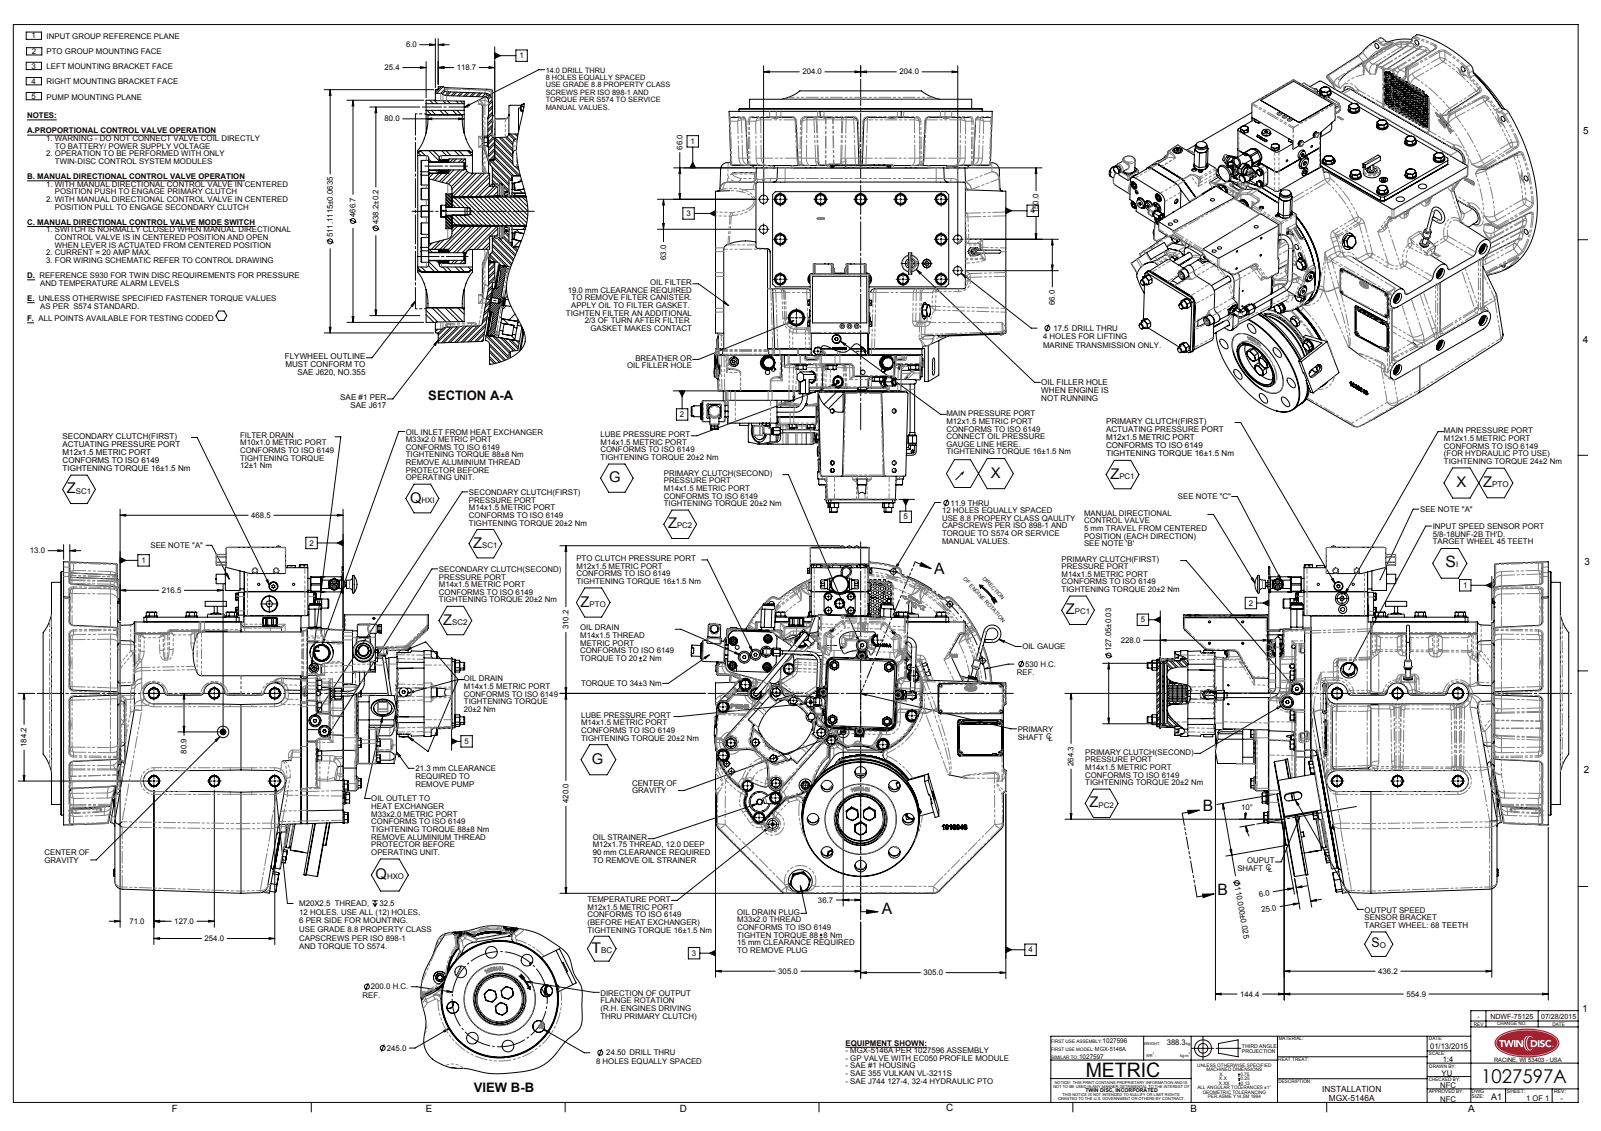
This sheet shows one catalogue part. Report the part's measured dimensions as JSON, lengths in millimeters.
{"part_name": "1027597A", "step_written_by": "SolidWorks 2010 (AUTOMOTIVE_DESIGN)", "units": "millimeters", "bodies": {"solids": 0, "faces": 5019, "planar": 1652, "cylindrical": 1588, "other": 1779}, "overall_size": [885.73, 730.22, 663.79], "round_holes": [[7, 90], [11.91, 12], [25, 9], [4.2, 8], [14, 8], [24.5, 8], [8.8, 6], [23.51, 6], [20, 5], [12, 4], [14.34, 4], [17.5, 4]], "round_bosses_or_shafts": [[24, 42], [18.9, 10], [6.35, 6], [19.05, 5], [16.8, 5], [13, 5], [12, 5], [2.54, 5]], "partial_cylinders_radius": [[3, 83], [8, 75], [2.5, 73], [6.5, 48], [16, 32], [2, 28], [3.05, 27], [6, 21]], "face_to_face_distances": [0.39, 13.09, 75, 75.39, 479.48, 404.48, 404.09, 88.48, 13.48, 391], "hole_center_spacings": [20, 10, 459.05, 20.07, 30, 34.68, 141.42, 26.51]}
